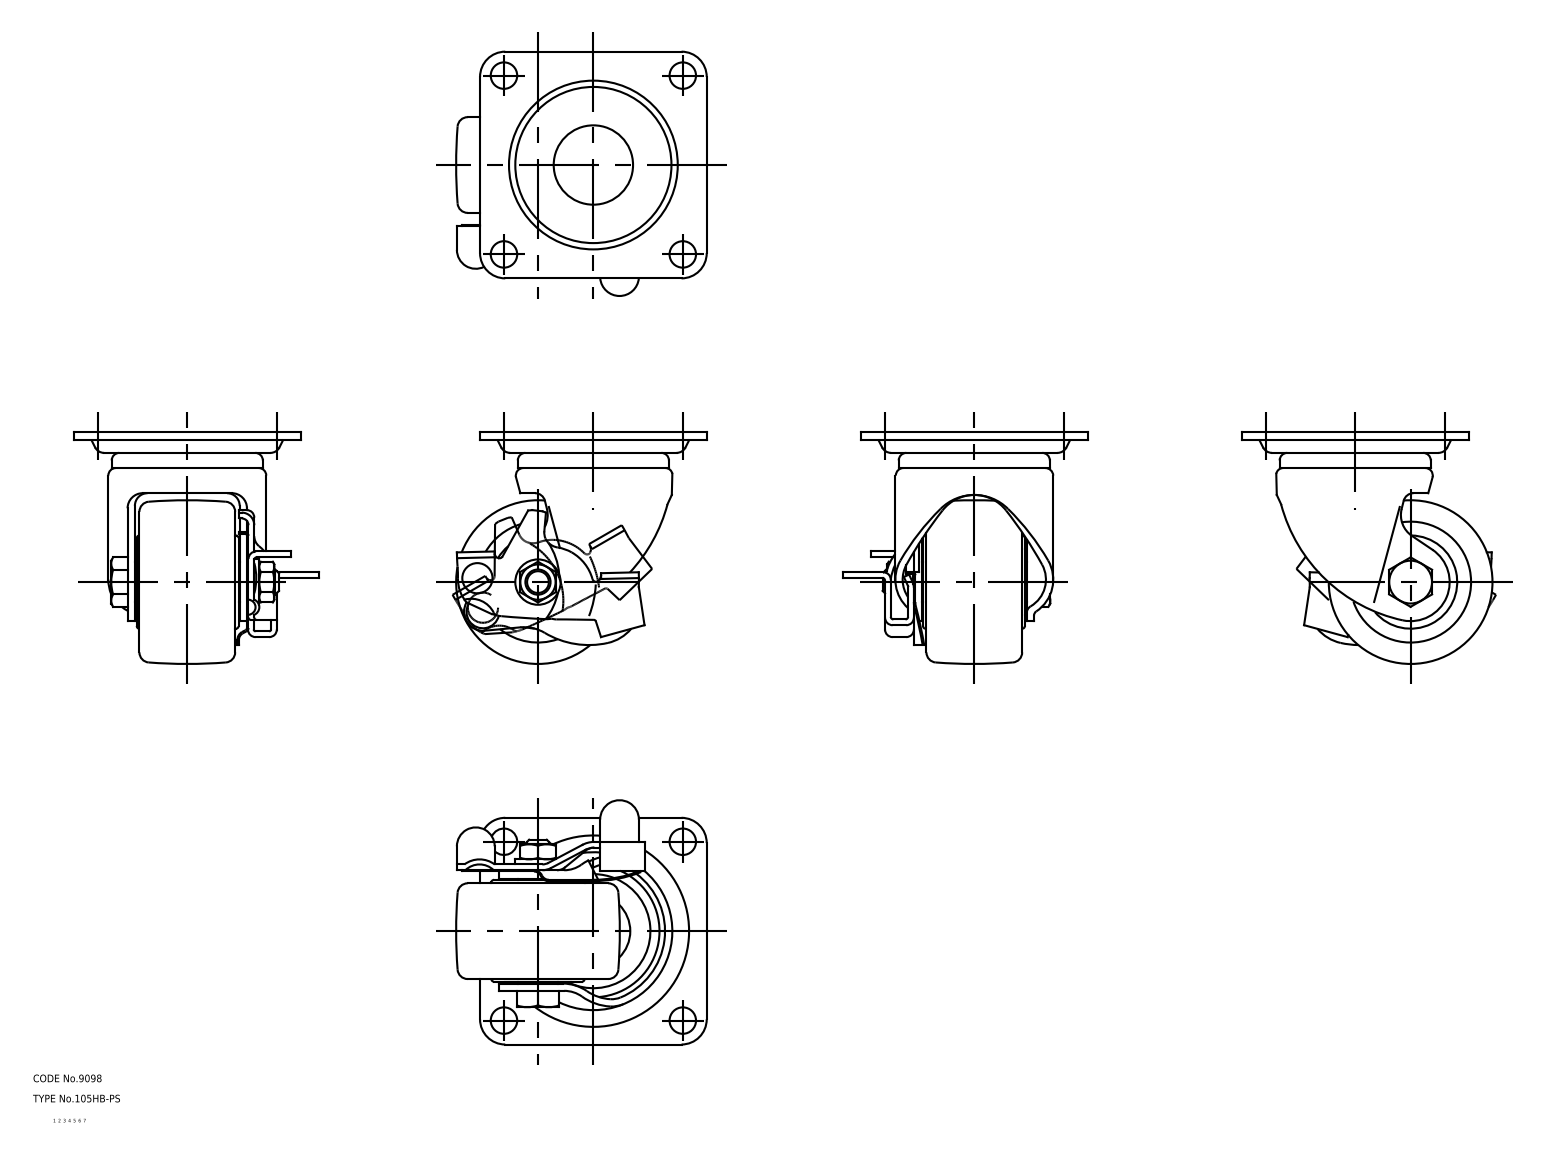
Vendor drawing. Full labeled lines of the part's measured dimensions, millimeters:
Part name (STEP PRODUCT): 67135742; 67135755; 67135768; 67135781 (+7 more)
STEP written by: CADfix (AUTOMOTIVE_DESIGN)
Units: millimetres
Bodies: 6 solids, 419 faces (0 planar, 0 cylindrical, 419 other)
Overall size (bounding box): 99.5 × 97 × 92
Volume: 226 445 mm³ · Surface area: 71 891 mm²
